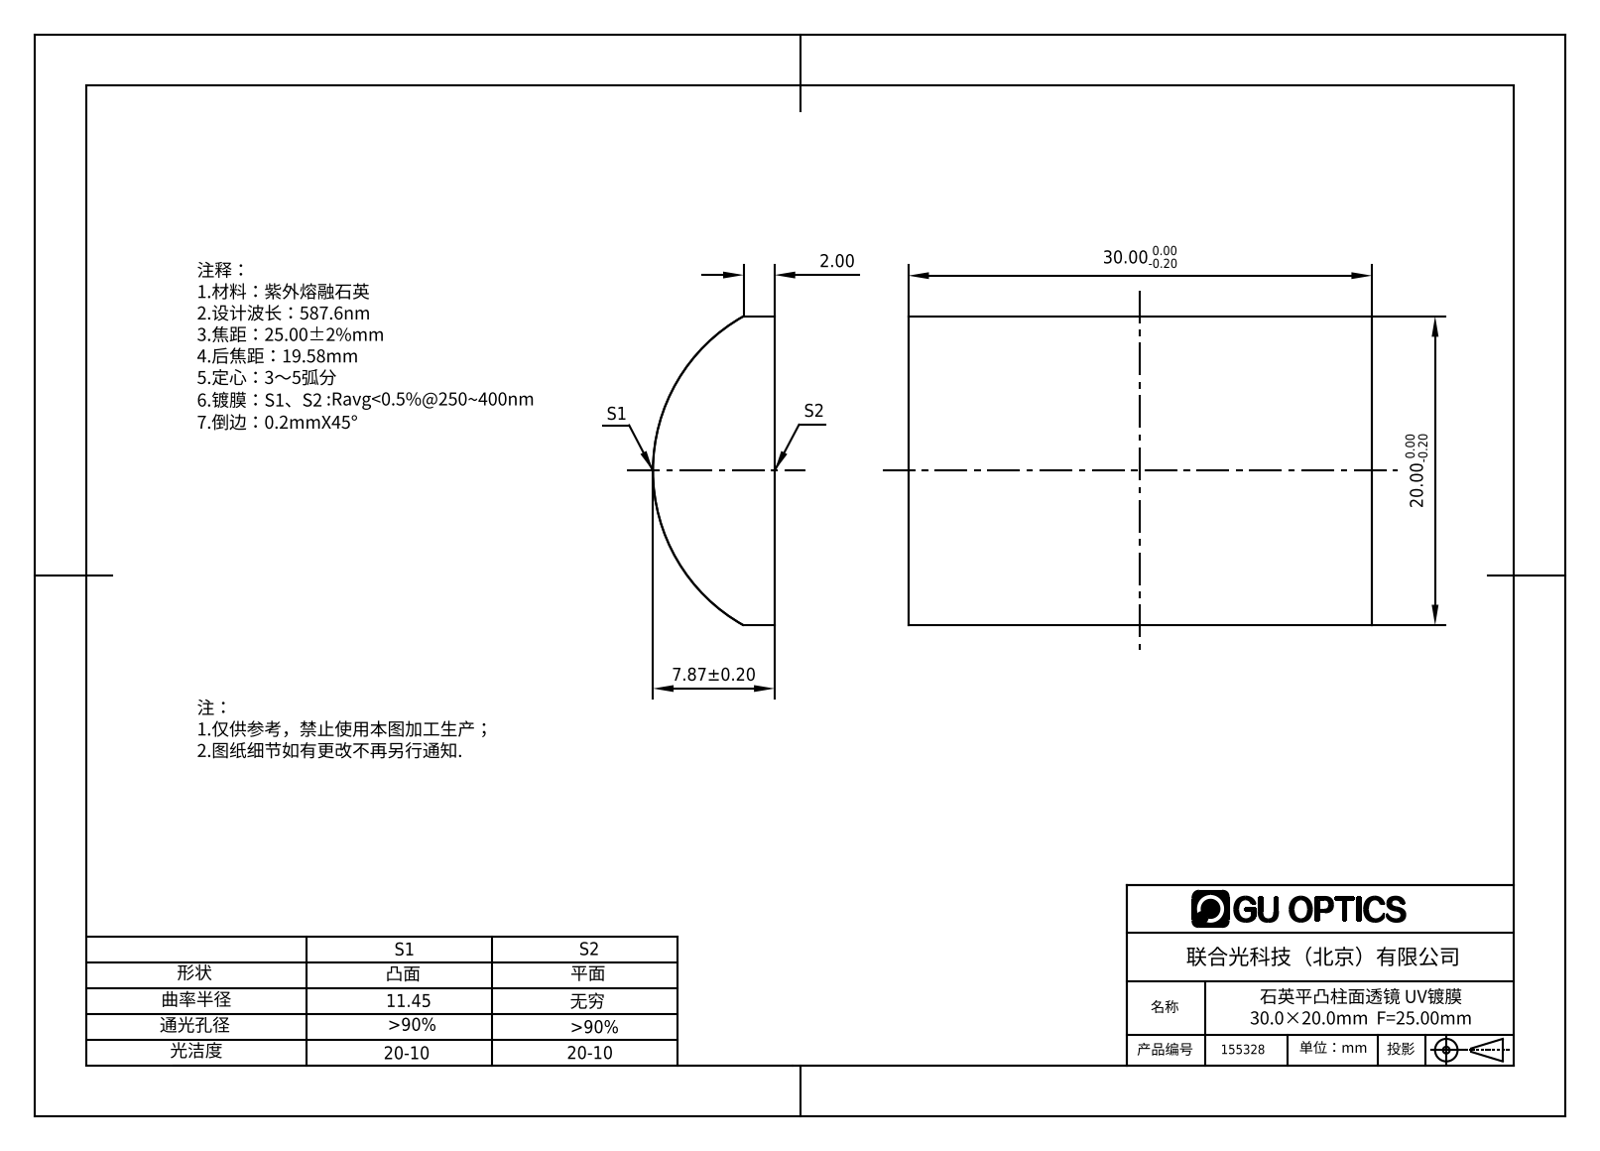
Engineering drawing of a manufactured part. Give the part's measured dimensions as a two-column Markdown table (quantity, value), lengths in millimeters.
| quantity | value |
| --- | --- |
| part name | 155294 |
| STEP written by | SolidWorks 2016 (AUTOMOTIVE_DESIGN) |
| units | millimeters |
| bodies | 1 solid, 6 faces (5 planar, 1 cylindrical, 0 other) |
| overall size | 30 × 20 × 7.87 |
| volume | 3 702 mm³ |
| surface area | 1 696 mm² |
| partial cylindrical surfaces (radius × count) | 11.45 × 1 |
| main face-to-face distances | 30, 20 |
